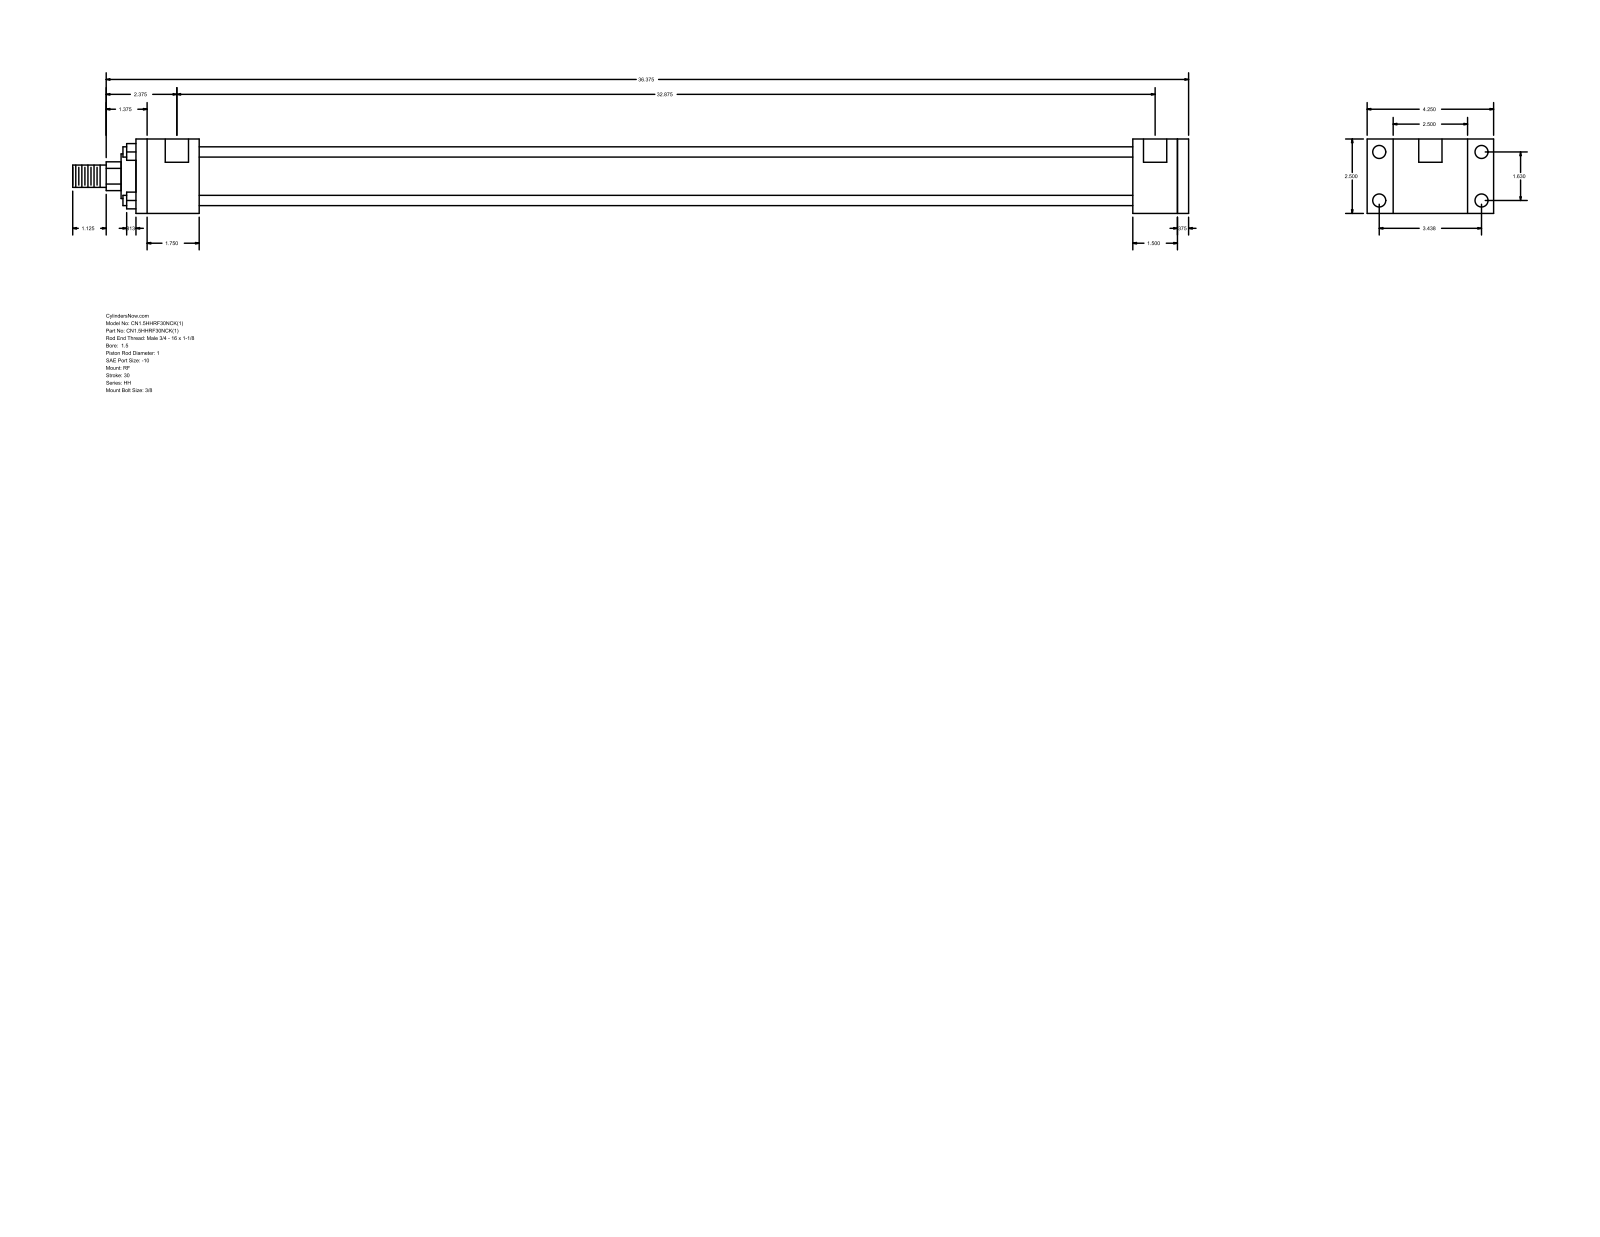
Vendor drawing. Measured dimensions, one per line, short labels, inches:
name: HH_RF__0150_1
written by: GSSL Pune (CONFIG_CONTROL_DESIGN)
unit: in
bodies: 0 solids, 92 faces (64 planar, 28 cylindrical, 0 other)
size: 37.5 × 4.25 × 2.5
holes: 4× ⌀0.219, 4× ⌀0.438, 2× ⌀0.781
bosses: 4× ⌀0.345, 1× ⌀1.75, 1× ⌀1.5, 1× ⌀1, 1× ⌀0.75
rounds: 1× R0.484
face distances: 2.5, 0.375, 1.5, 31.375, 32.875, 33.25, 1.875, 2.125, 33.5, 35
hole spacings: 0.063, 1.63, 3.438, 3.805, 32.937, 33, 32.875
